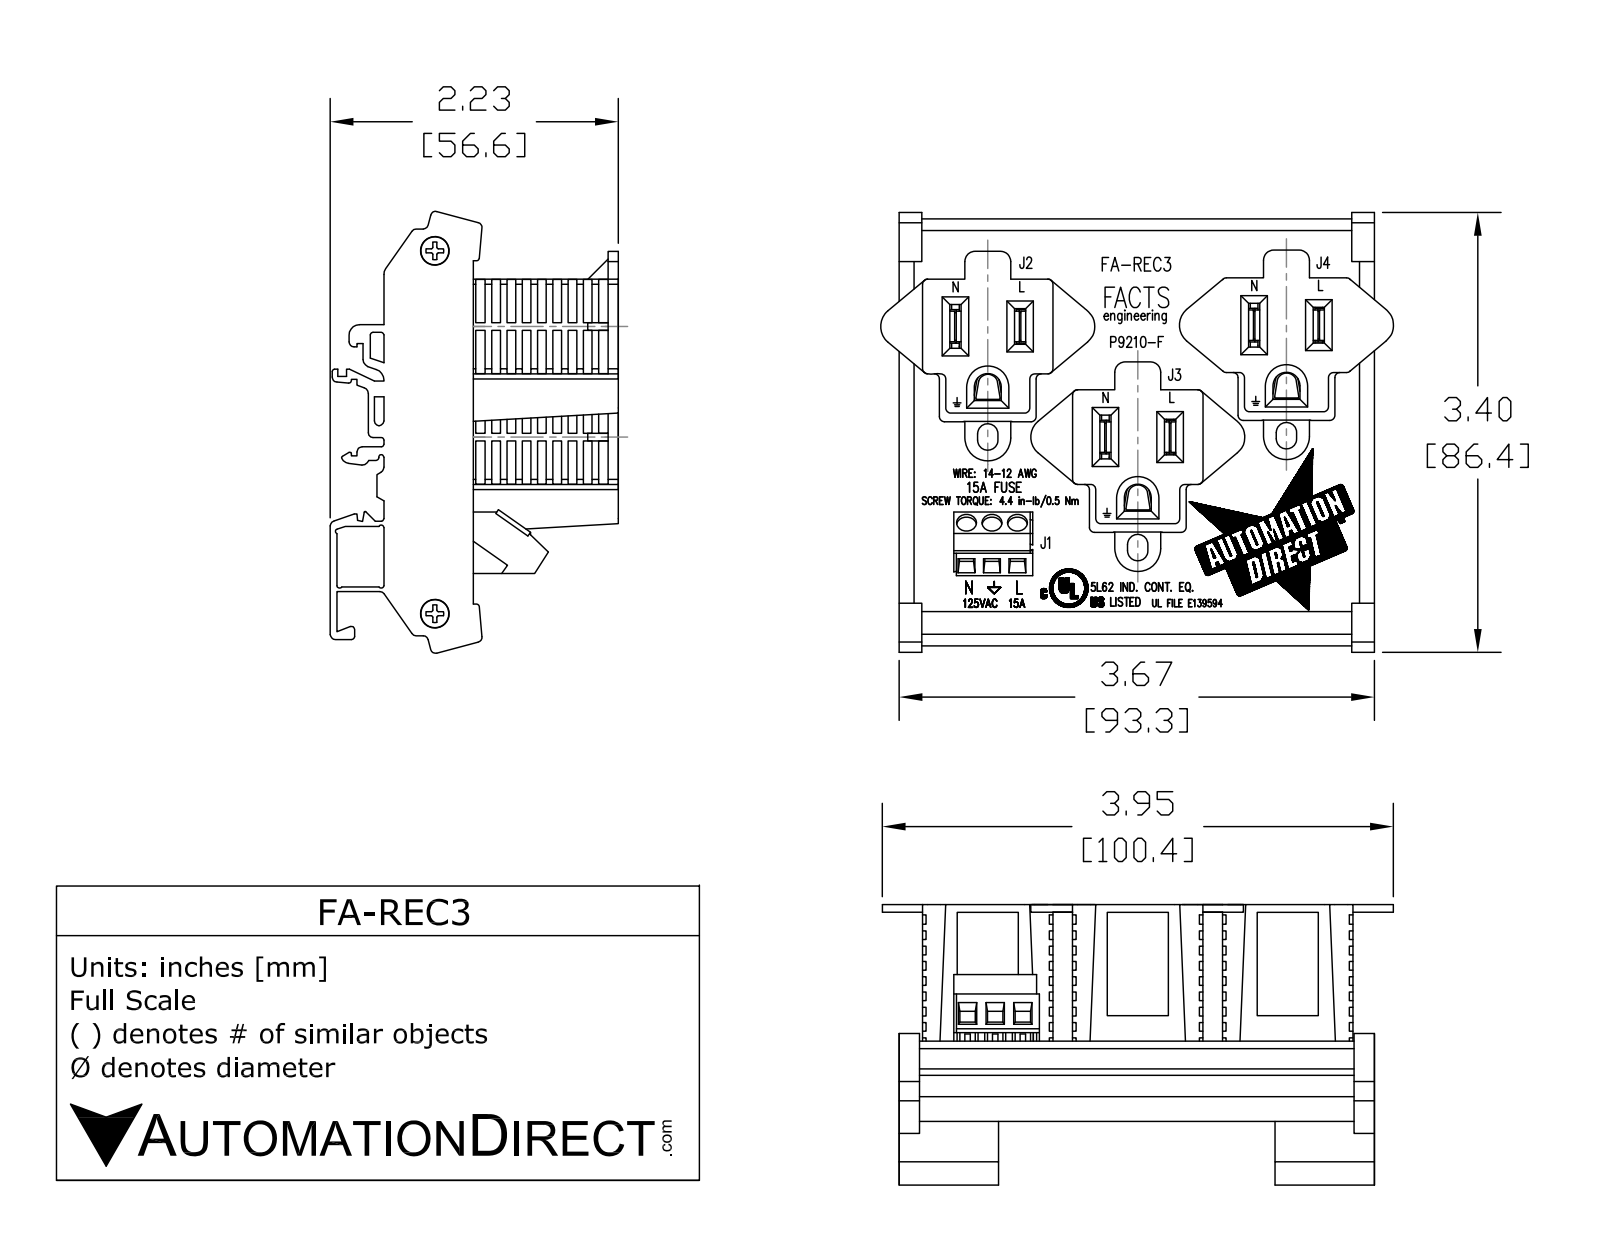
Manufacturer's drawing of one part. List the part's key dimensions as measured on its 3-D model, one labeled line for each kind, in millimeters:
Part name (STEP PRODUCT): FA-REC3
STEP written by: SolidWorks 2017 (AUTOMOTIVE_DESIGN)
Units: millimetres
Bodies: 2 solids, 561 faces (427 planar, 126 cylindrical, 8 other)
Overall size (bounding box): 93.4 × 86.79 × 56.62
Volume: 184 789 mm³ · Surface area: 41 169 mm²
Round holes (diameter × count): ⌀3.5 ×3
Partial cylindrical surfaces — rounded edges, fillets, slot ends (radius × count): R0.52 ×3, R2.64 ×3, R0.5 ×2, R0.53 ×2, R0.98 ×2, R0.18 ×1, R0.32 ×1, R0.32 ×1
Main face-to-face distances: 16.55, 0.5, 45.54, 17.05, 28.99, 93.4, 25.63, 58.69, 46.04, 26.3
Hole centre spacings: 5, 10
